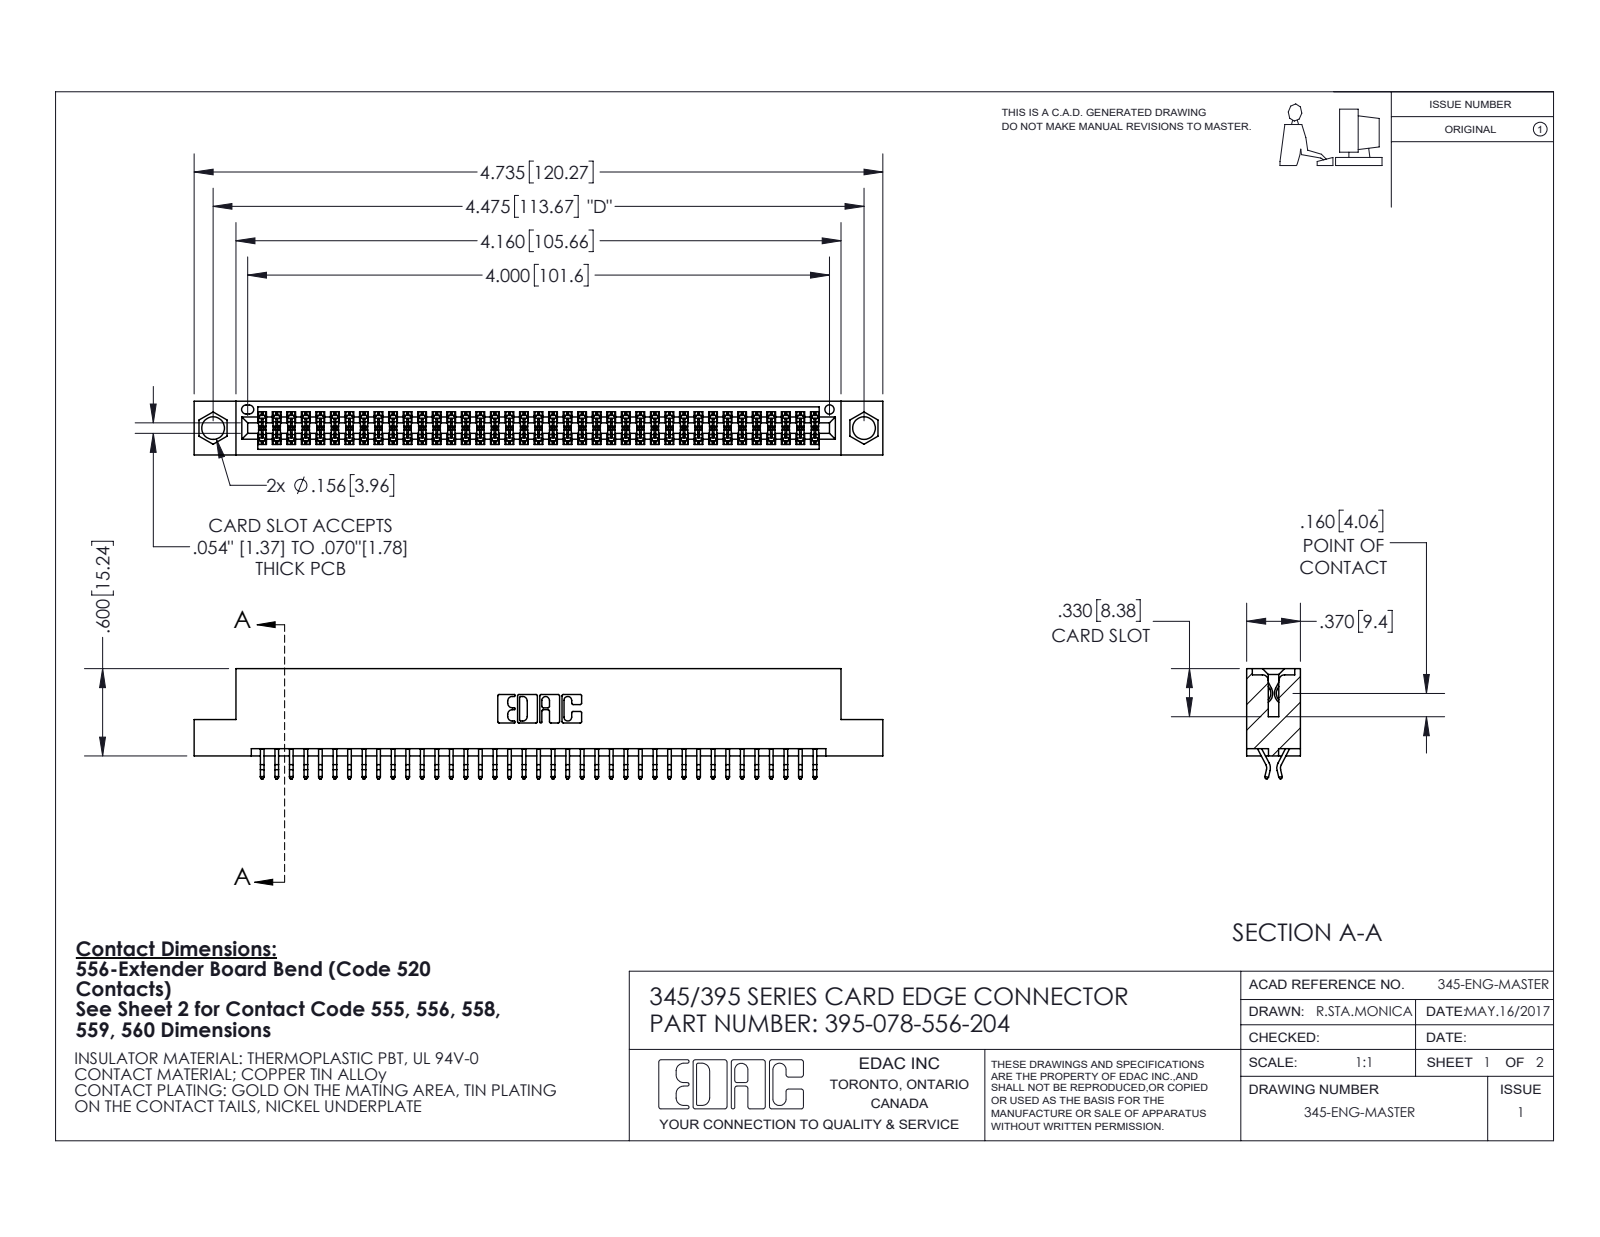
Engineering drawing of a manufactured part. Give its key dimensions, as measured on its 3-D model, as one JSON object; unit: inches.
{"part_name": "395-078-556-204; 345-292-001_556 Tail; 345 Part_Flush Mounting Lugs - 0.156 Dia-TI", "step_written_by": "SolidWorks 2020 (CONFIG_CONTROL_DESIGN)", "units": "inches", "bodies": {"solids": 79, "faces": 4508, "planar": 2980, "cylindrical": 1528, "other": 0}, "overall_size": [4.735, 0.757, 0.37], "volume_in3": 0.705, "surface_area_in2": 26.03, "round_holes": [[0.156, 2], [0.064, 1]], "partial_cylinders_radius": [[0.006, 156], [0.01, 22], [0.007, 6], [0.031, 6], [0.026, 3], [0.01, 2], [0.014, 2], [0.019, 2]], "face_to_face_distances": [0.298, 0.072, 0.37, 0.2, 0.025, 0.098, 0.272, 0.225, 0.175, 0.149], "hole_center_spacings": [0.27, 4.239, 4.475]}
